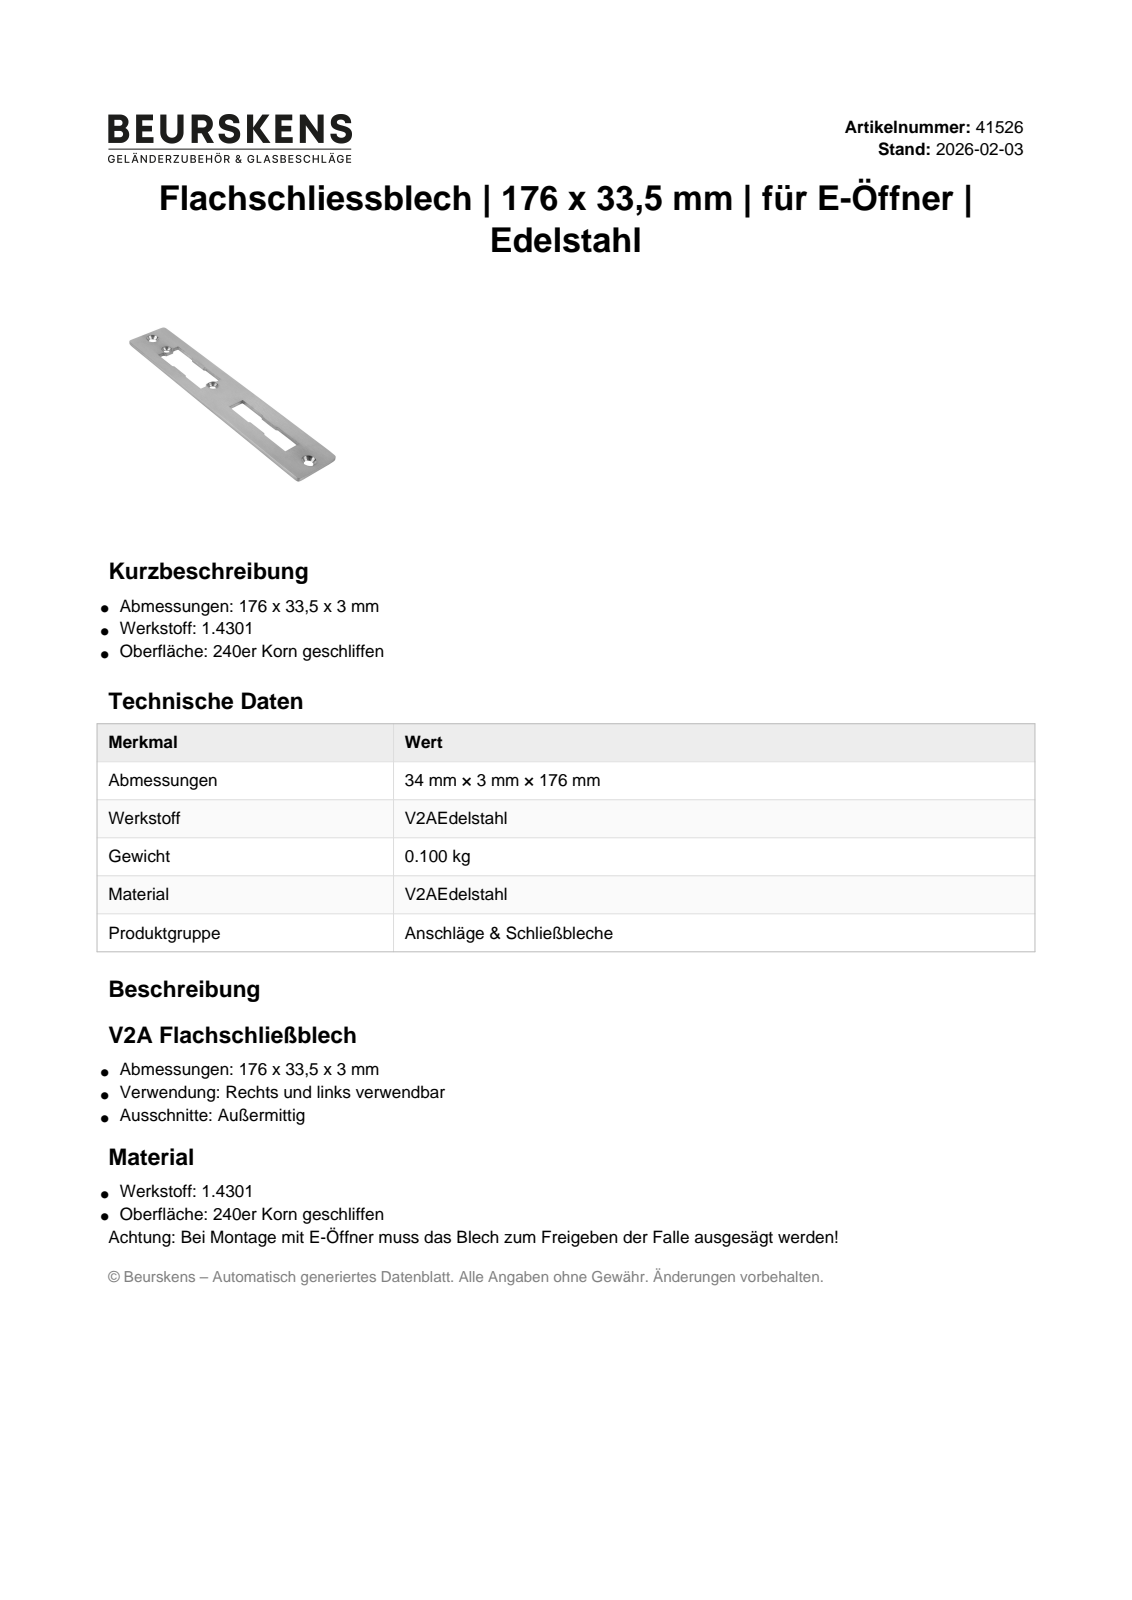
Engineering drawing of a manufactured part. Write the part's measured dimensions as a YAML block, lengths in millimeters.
part_name: "41526"
step_written_by: "SolidWorks 2020 (CONFIG_CONTROL_DESIGN)"
units: millimeters
bodies: {solids: 1, faces: 58, planar: 38, cylindrical: 12, other: 8}
overall_size: [176, 33.5, 3]
volume: 13108
surface_area: 11000
round_holes:
  - {diameter: 4.5, count: 2}
  - {diameter: 5.5, count: 2}
partial_cylinders:
  - {radius: 2, count: 4}
face_to_face_distances: [3, 33.5, 10.75, 22.75, 7.75, 25.75, 15, 1, 14, 12]
hole_center_spacings: [17, 52, 69, 91, 143, 160]
